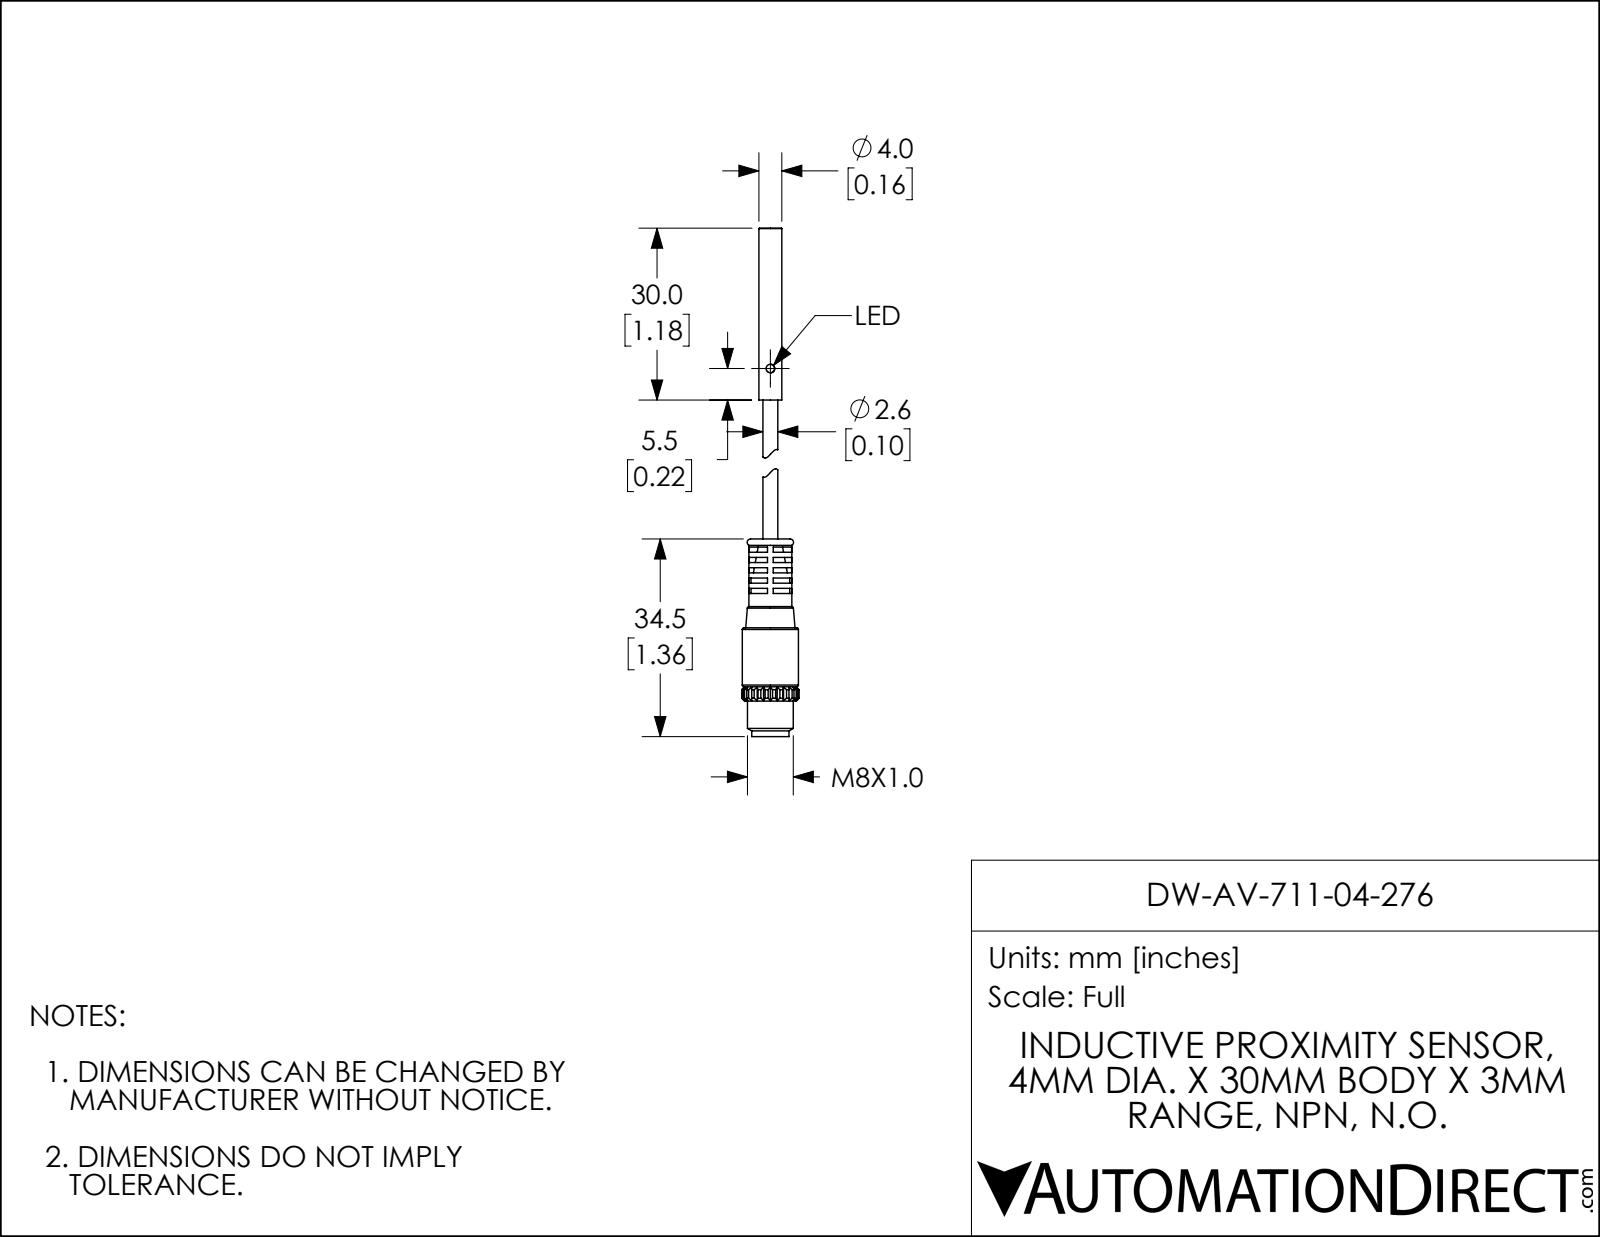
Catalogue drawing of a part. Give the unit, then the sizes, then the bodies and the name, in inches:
Units: inches
Overall size (bounding box): 3.494 × 0.393 × 0.393
Round holes (diameter × count): ⌀0.059 ×1, ⌀0.228 ×1
Round bosses / shafts (diameter × count): ⌀0.039 ×3, ⌀0.386 ×1, ⌀0.315 ×1, ⌀0.295 ×1, ⌀0.269 ×1, ⌀0.256 ×1, ⌀0.157 ×1, ⌀0.138 ×1
Partial cylindrical surfaces — rounded edges, fillets, slot ends (radius × count): R0.075 ×1, R0.197 ×1
Main face-to-face distances: 0.035, 0.071, 0.106, 0.142, 0.177, 0.213, 1.161, 0.056, 1.106, 0.091
Volume: 0.145 in³ · Surface area: 3.062 in²
Bodies: 2 solids, 212 faces (139 planar, 45 cylindrical, 28 other)
Part name (STEP PRODUCT): DW-AV-711-04-276
STEP written by: SolidWorks 2017 (AUTOMOTIVE_DESIGN)
